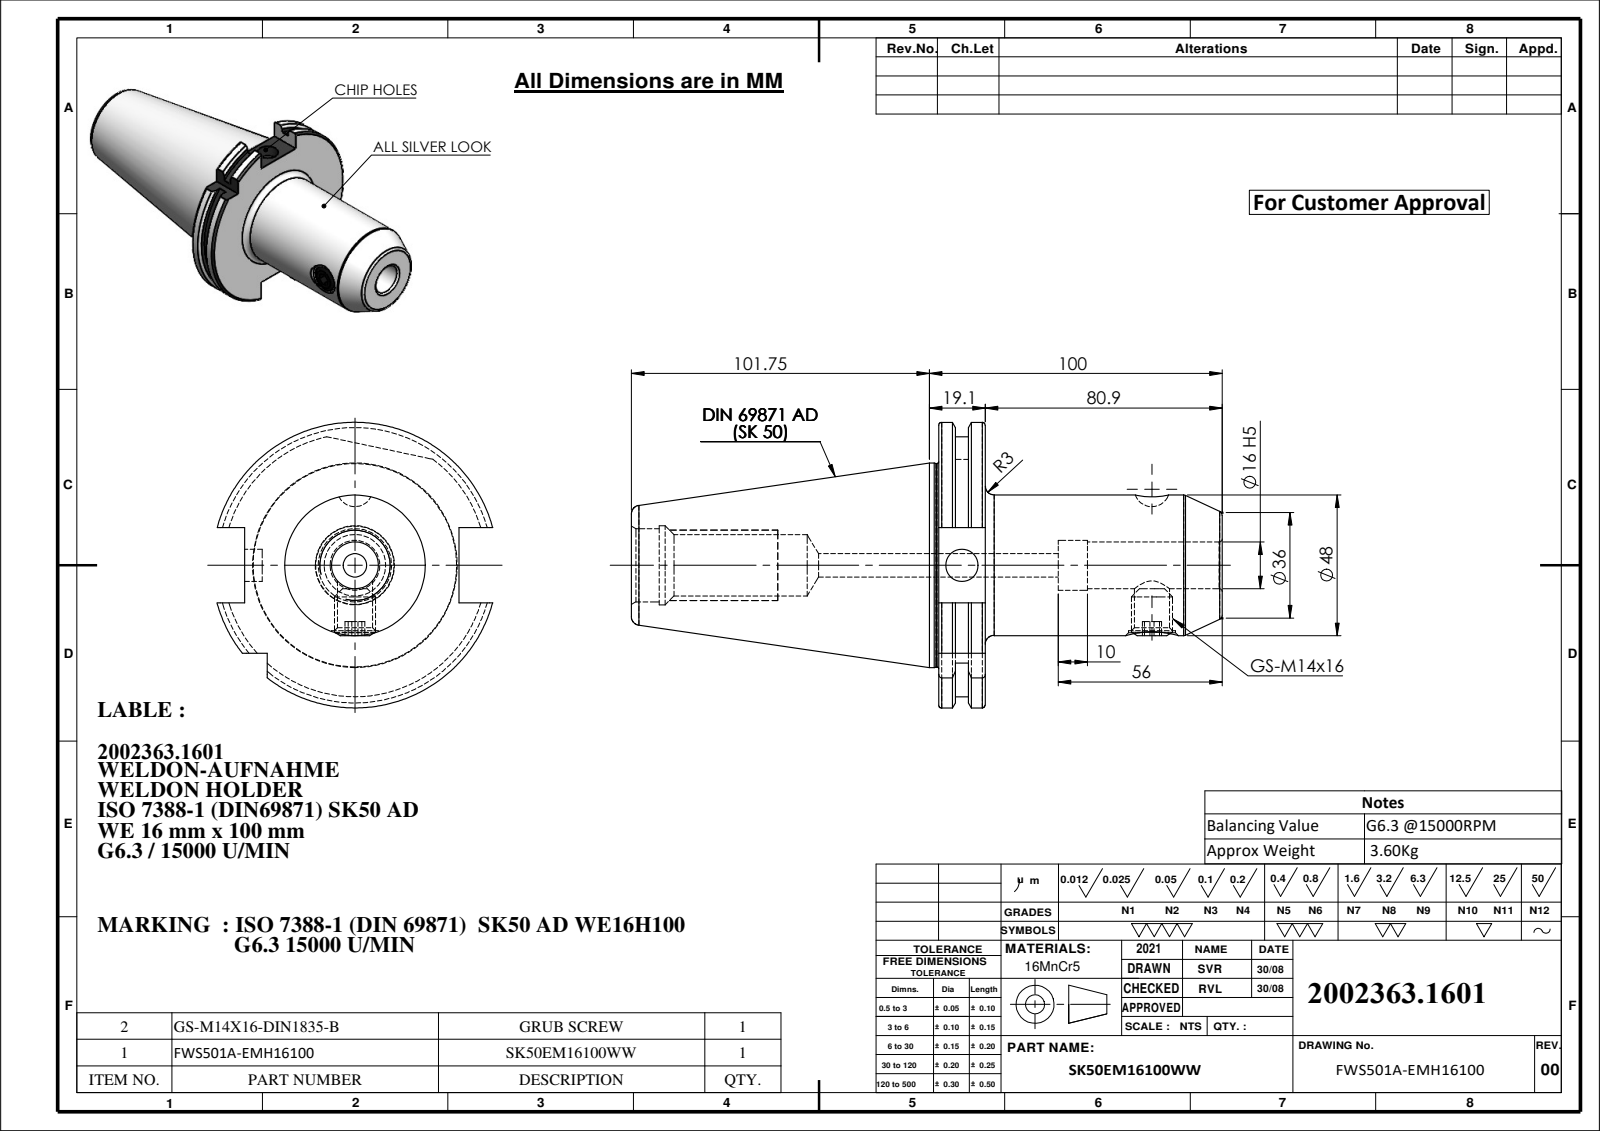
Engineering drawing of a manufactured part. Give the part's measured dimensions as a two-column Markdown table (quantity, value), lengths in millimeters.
| quantity | value |
| --- | --- |
| part name | SK50EM16100WW; FWS501A-EMH16100; GS-M14X16-DIN1835-B_ISO 4026 - M12 x 12-N |
| STEP written by | SolidWorks 2024 (CONFIG_CONTROL_DESIGN) |
| units | millimeters |
| bodies | 2 solids, 125 faces (33 planar, 39 cylindrical, 53 other) |
| overall size | 201.75 × 97.5 × 94.05 |
| volume | 464 764 mm³ |
| surface area | 58 010 mm² |
| round holes (diameter × count) | 16 × 2, 8 × 1, 11 × 1, 12 × 1, 17 × 1, 21 × 1, 25 × 1, 27 × 1 |
| round bosses / shafts (diameter × count) | 69.85 × 1, 69.45 × 1, 48 × 1, 14 × 1 |
| partial cylindrical surfaces (radius × count) | 44.9 × 1, 48.75 × 1 |
| main face-to-face distances | 15.9, 96.8, 80.9, 5.66, 10.24, 91.14, 10.15, 4.49, 5.75, 86.65 |
